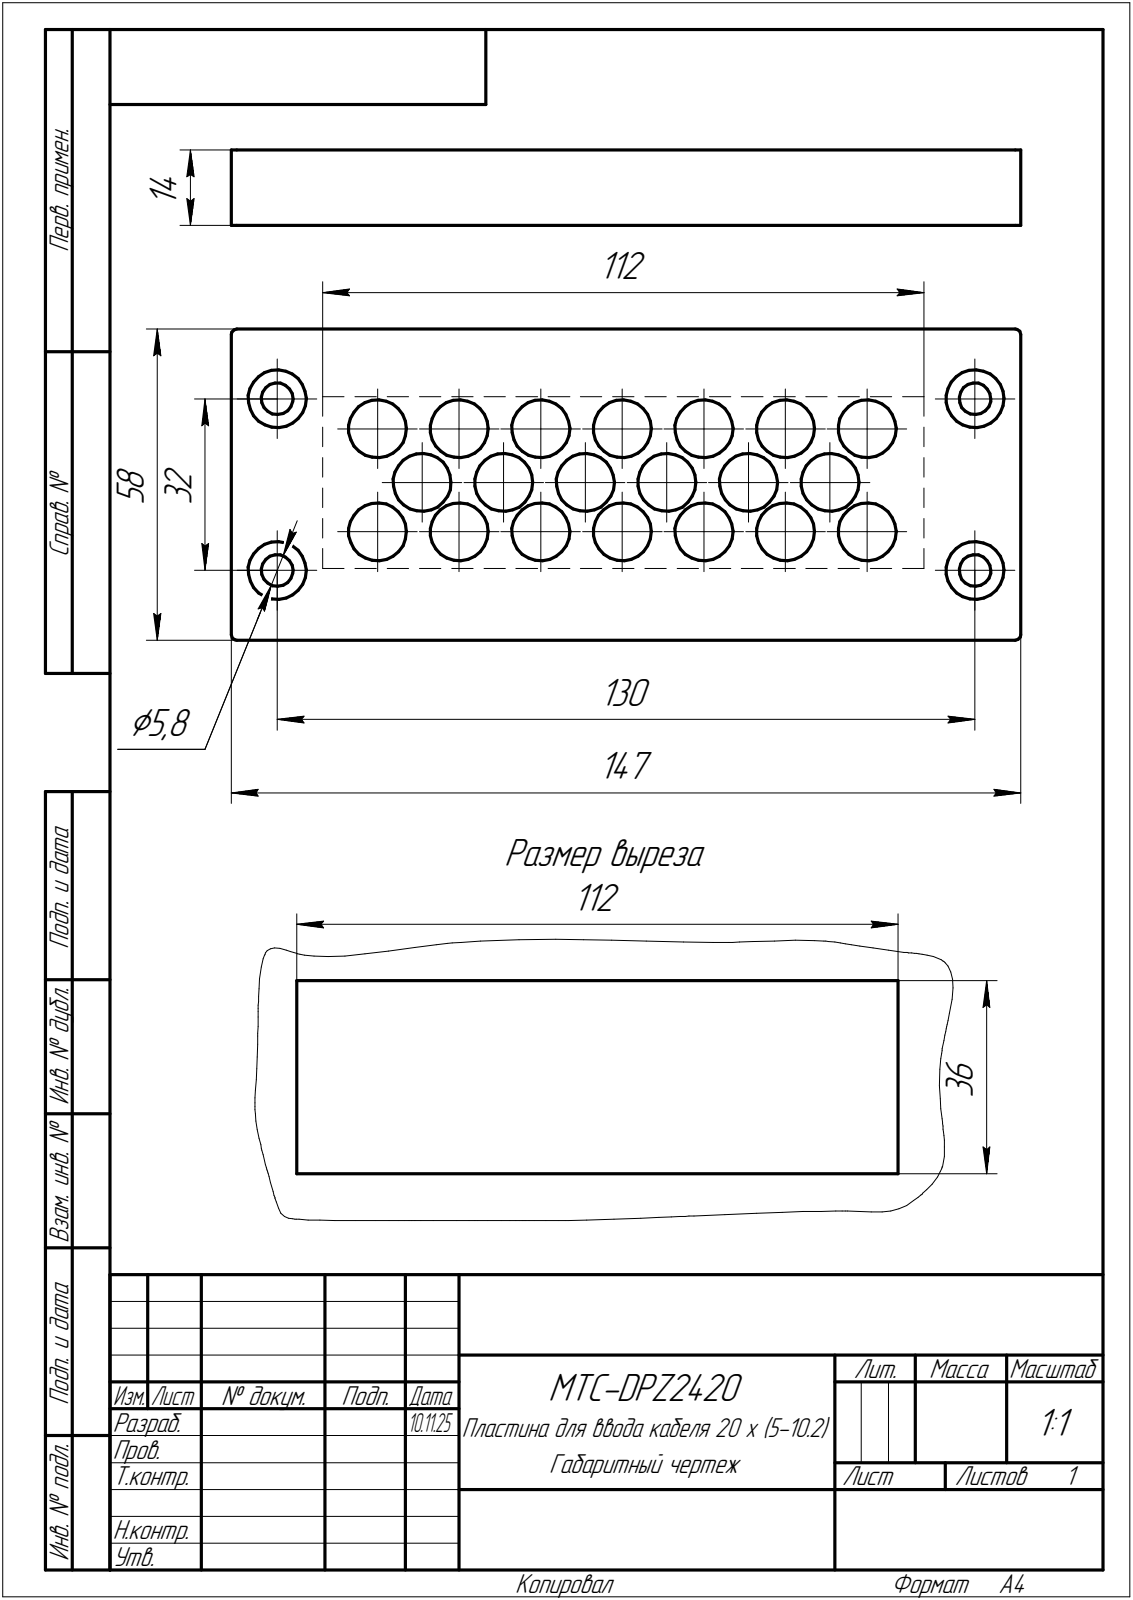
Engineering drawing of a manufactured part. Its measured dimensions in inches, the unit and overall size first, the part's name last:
Units: inches
Overall size (bounding box): 5.787 × 2.283 × 0.551
Round holes (diameter × count): ⌀0.425 ×24, ⌀0.232 ×4
Partial cylindrical surfaces — rounded edges, fillets, slot ends (radius × count): R0.039 ×4
Main face-to-face distances: 0.551, 0.512, 0.315, 0.236, 0.039, 0.197, 2.283, 1.772, 1.26, 5.787
Hole centre spacings: 0.598, 1.197, 0.964, 1.795, 1.416, 1.948, 2.394, 0.756
Volume: 5.25 in³ · Surface area: 41.66 in²
Bodies: 1 solid, 67 faces (35 planar, 32 cylindrical, 0 other)
Part name (STEP PRODUCT): MTC-DPZ2420
STEP written by: C3D Toolkit (CONFIG_CONTROL_DESIGN)
